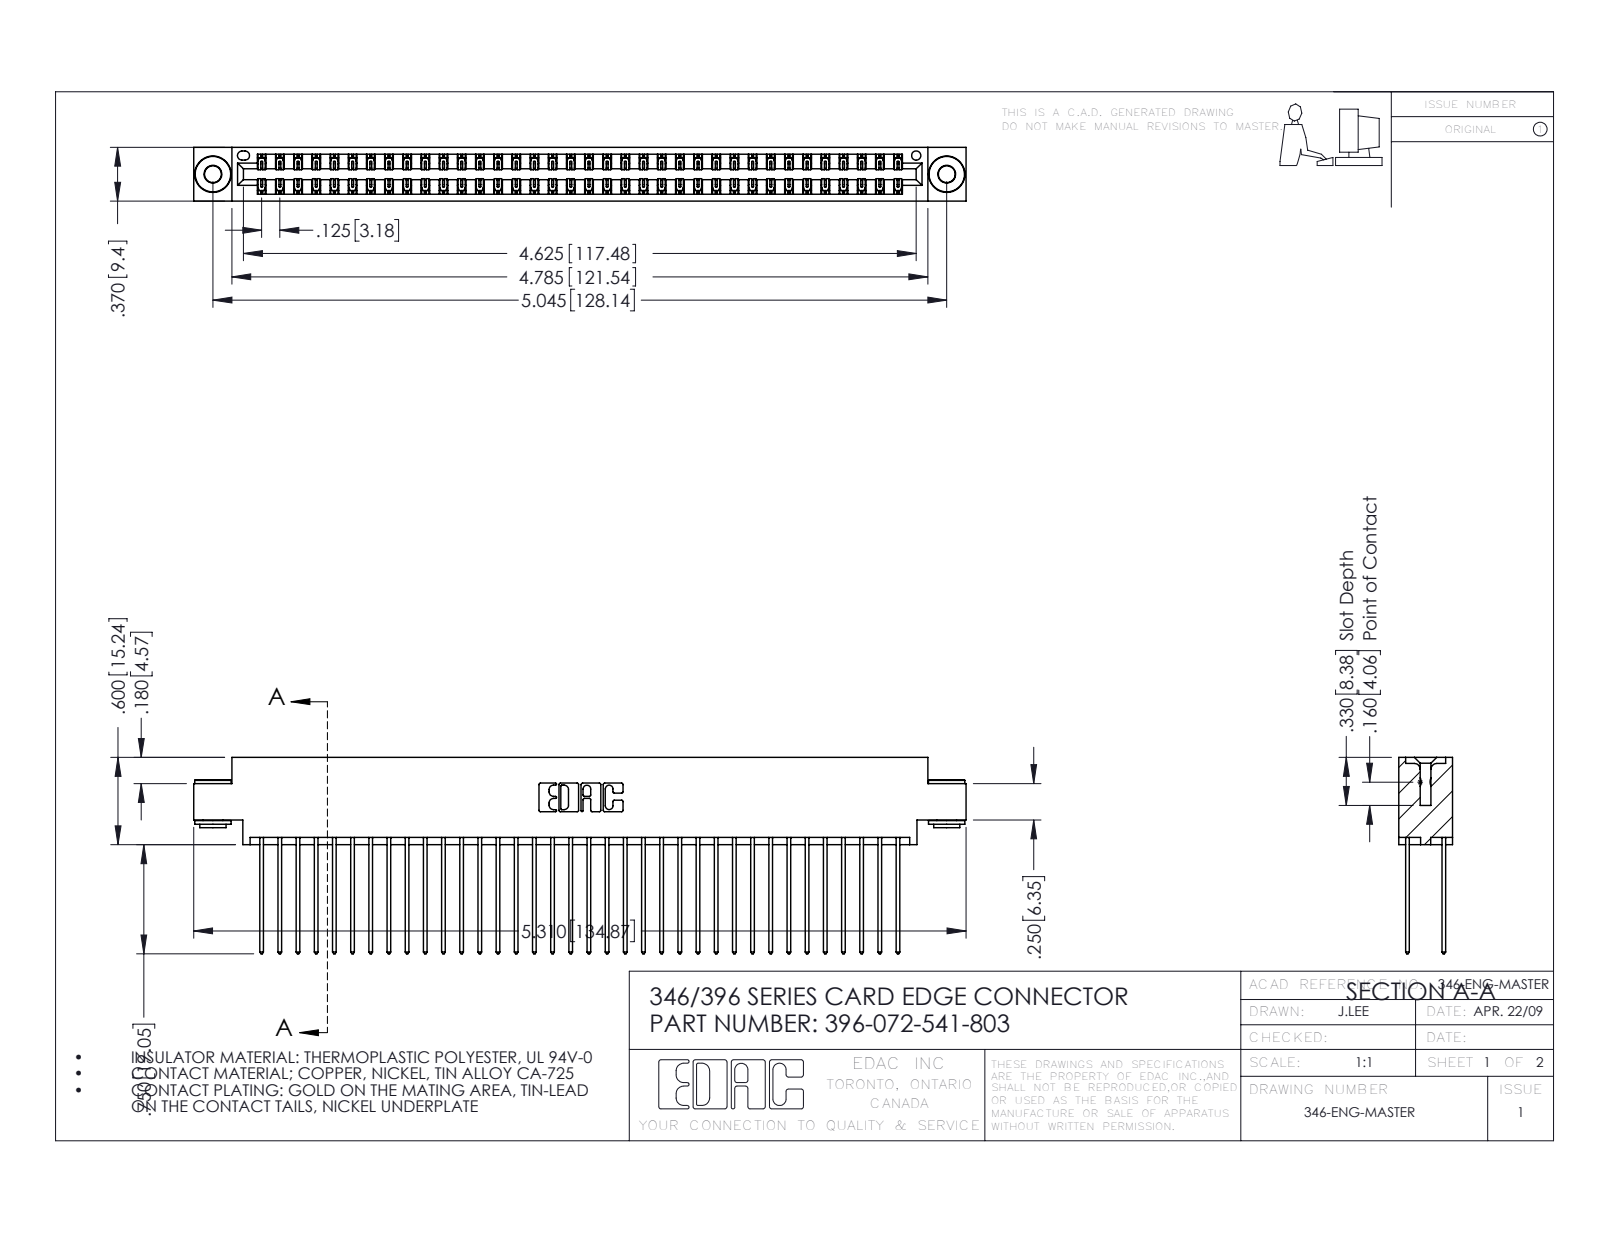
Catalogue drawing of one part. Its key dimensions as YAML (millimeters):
part_name: "345-250-002_345-250-002-102; 396-072-541-803; 346 Part_0.170 Offset - 0.156 Dia-TH; 345-292-001_345-293-141"
step_written_by: "SolidWorks 2016 (CONFIG_CONTROL_DESIGN)"
units: millimeters
bodies: {solids: 75, faces: 3908, planar: 2610, cylindrical: 1290, other: 8}
overall_size: [134.9, 34.3, 9.4]
volume: 13400
surface_area: 20680
round_holes:
  - {diameter: 2.9, count: 2}
  - {diameter: 4, count: 2}
  - {diameter: 1.6, count: 1}
round_bosses_or_shafts:
  - {diameter: 6.4, count: 2}
  - {diameter: 4.6, count: 2}
  - {diameter: 3.5, count: 2}
partial_cylinders:
  - {radius: 0.2, count: 108}
  - {radius: 0.3, count: 72}
  - {radius: 0.3, count: 22}
  - {radius: 0.2, count: 6}
  - {radius: 0.8, count: 6}
  - {radius: 0.7, count: 3}
  - {radius: 0.4, count: 2}
  - {radius: 0.6, count: 2}
face_to_face_distances: [1.2, 8.2, 6.4, 0.6, 1.8, 7.6, 9.4, 7, 5.7, 3.8]
hole_center_spacings: [6.2, 122.8, 128.1]
